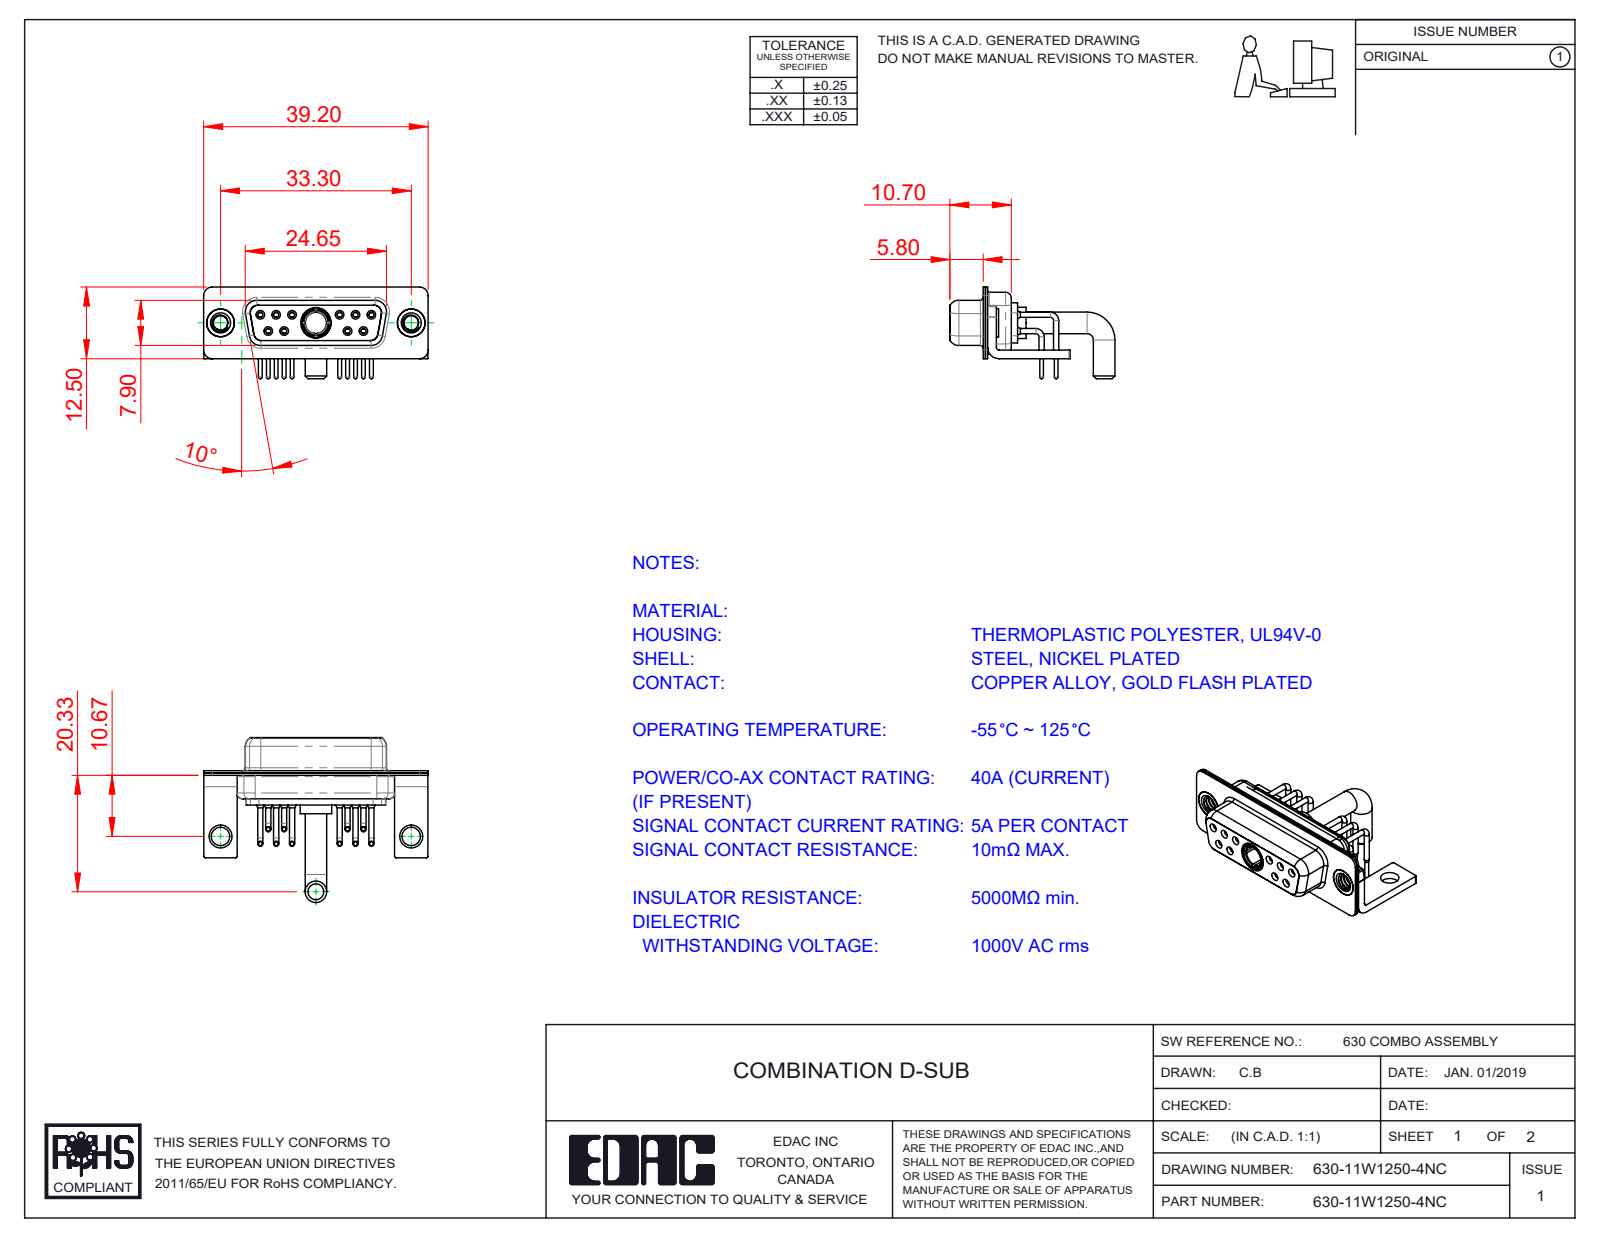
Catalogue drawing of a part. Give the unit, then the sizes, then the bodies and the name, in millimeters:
Units: millimetres
Overall size (bounding box): 39.2 × 28.8 × 16
Round holes (diameter × count): ⌀0.9 ×10, ⌀1.1 ×10, ⌀1.5 ×10, ⌀2 ×10, ⌀1.7 ×6, ⌀1.6 ×4, ⌀4.85 ×3, ⌀2.5 ×2, ⌀3.2 ×2, ⌀4 ×2, ⌀4.05 ×2, ⌀3.7 ×1
Round bosses / shafts (diameter × count): ⌀0.9 ×10, ⌀0.65 ×10, ⌀1.6 ×6, ⌀5 ×2, ⌀4.95 ×2, ⌀4.8 ×2, ⌀3.75 ×2, ⌀5.5 ×1
Partial cylindrical surfaces — rounded edges, fillets, slot ends (radius × count): R0.25 ×16, R1.5 ×16, R2 ×13, R1.35 ×12, R1.6 ×8, R0.5 ×5, R0.6 ×4, R0.65 ×4
Main face-to-face distances: 0.4, 0.8, 1.4, 0.45, 8.45, 1.5, 1.8, 8.9, 6.2, 2.3
Hole centre spacings: 3.16, 2.77, 13.85, 11.08, 16.62, 5.03, 5.04, 5.54
Volume: 3 059 mm³ · Surface area: 6 988 mm²
Bodies: 19 solids, 925 faces (266 planar, 410 cylindrical, 249 other)
Part name (STEP PRODUCT): 630Combo Housing_11W1; 630Combo Contact Row 2; 630Combo Shell Rear_15 Contacts; 630Combo Shell Front_15 Contacts (+5 more)
STEP written by: SolidWorks 2020 (CONFIG_CONTROL_DESIGN)
